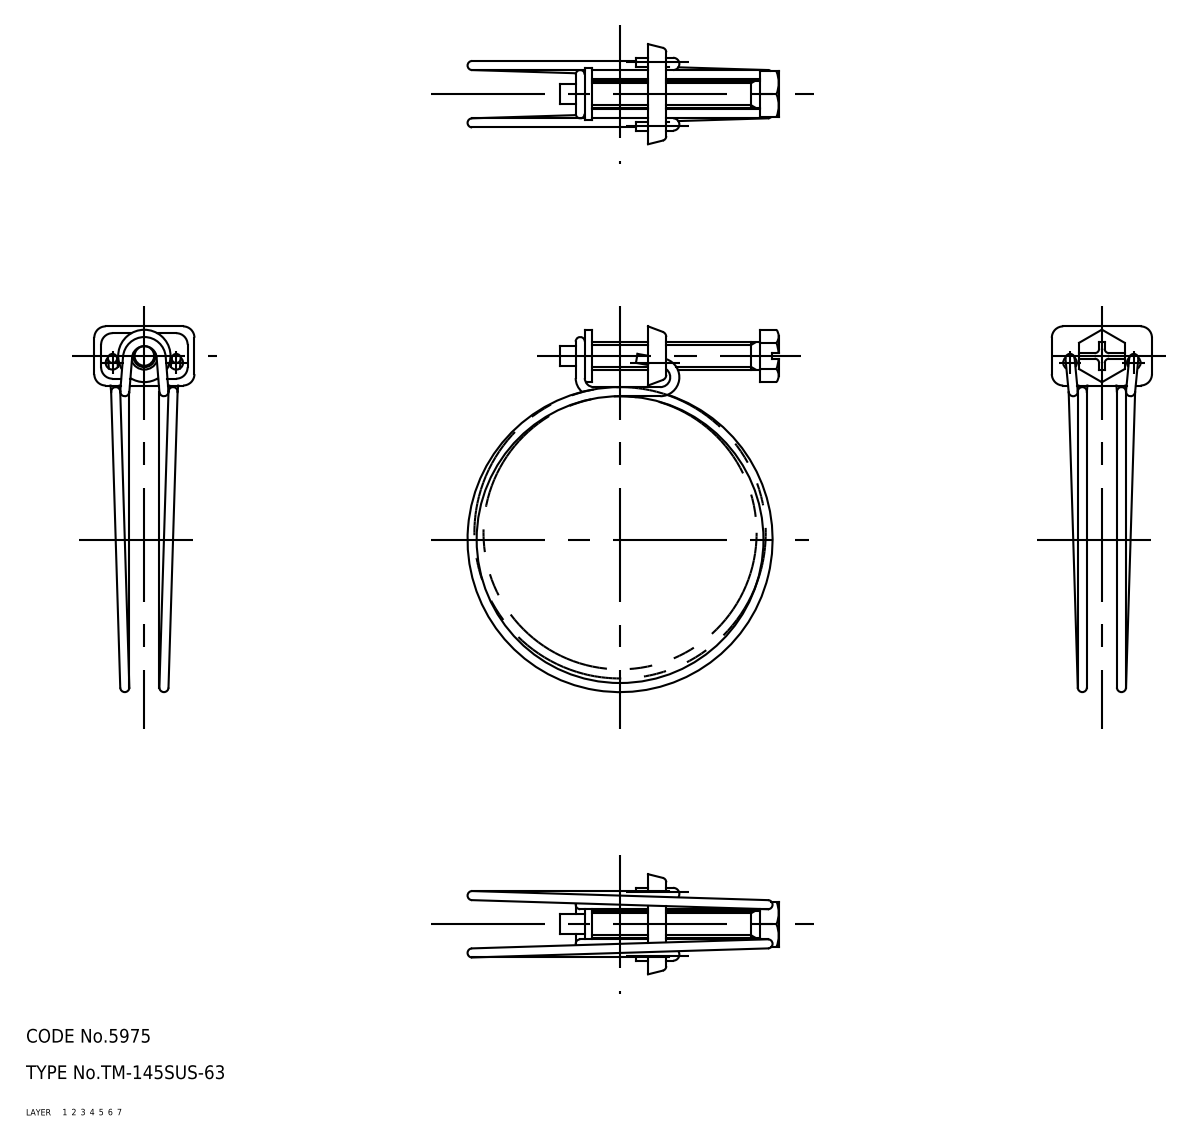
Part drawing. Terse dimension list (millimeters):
name: screw; holder; band; TM_145SUS_63_22513_36
written by: CADfix (AUTOMOTIVE_DESIGN)
unit: mm
bodies: 3 solids, 119 faces (0 planar, 0 cylindrical, 119 other)
size: 80.35 × 68.35 × 22
volume: 3 668 mm³; area: 5 271 mm²
